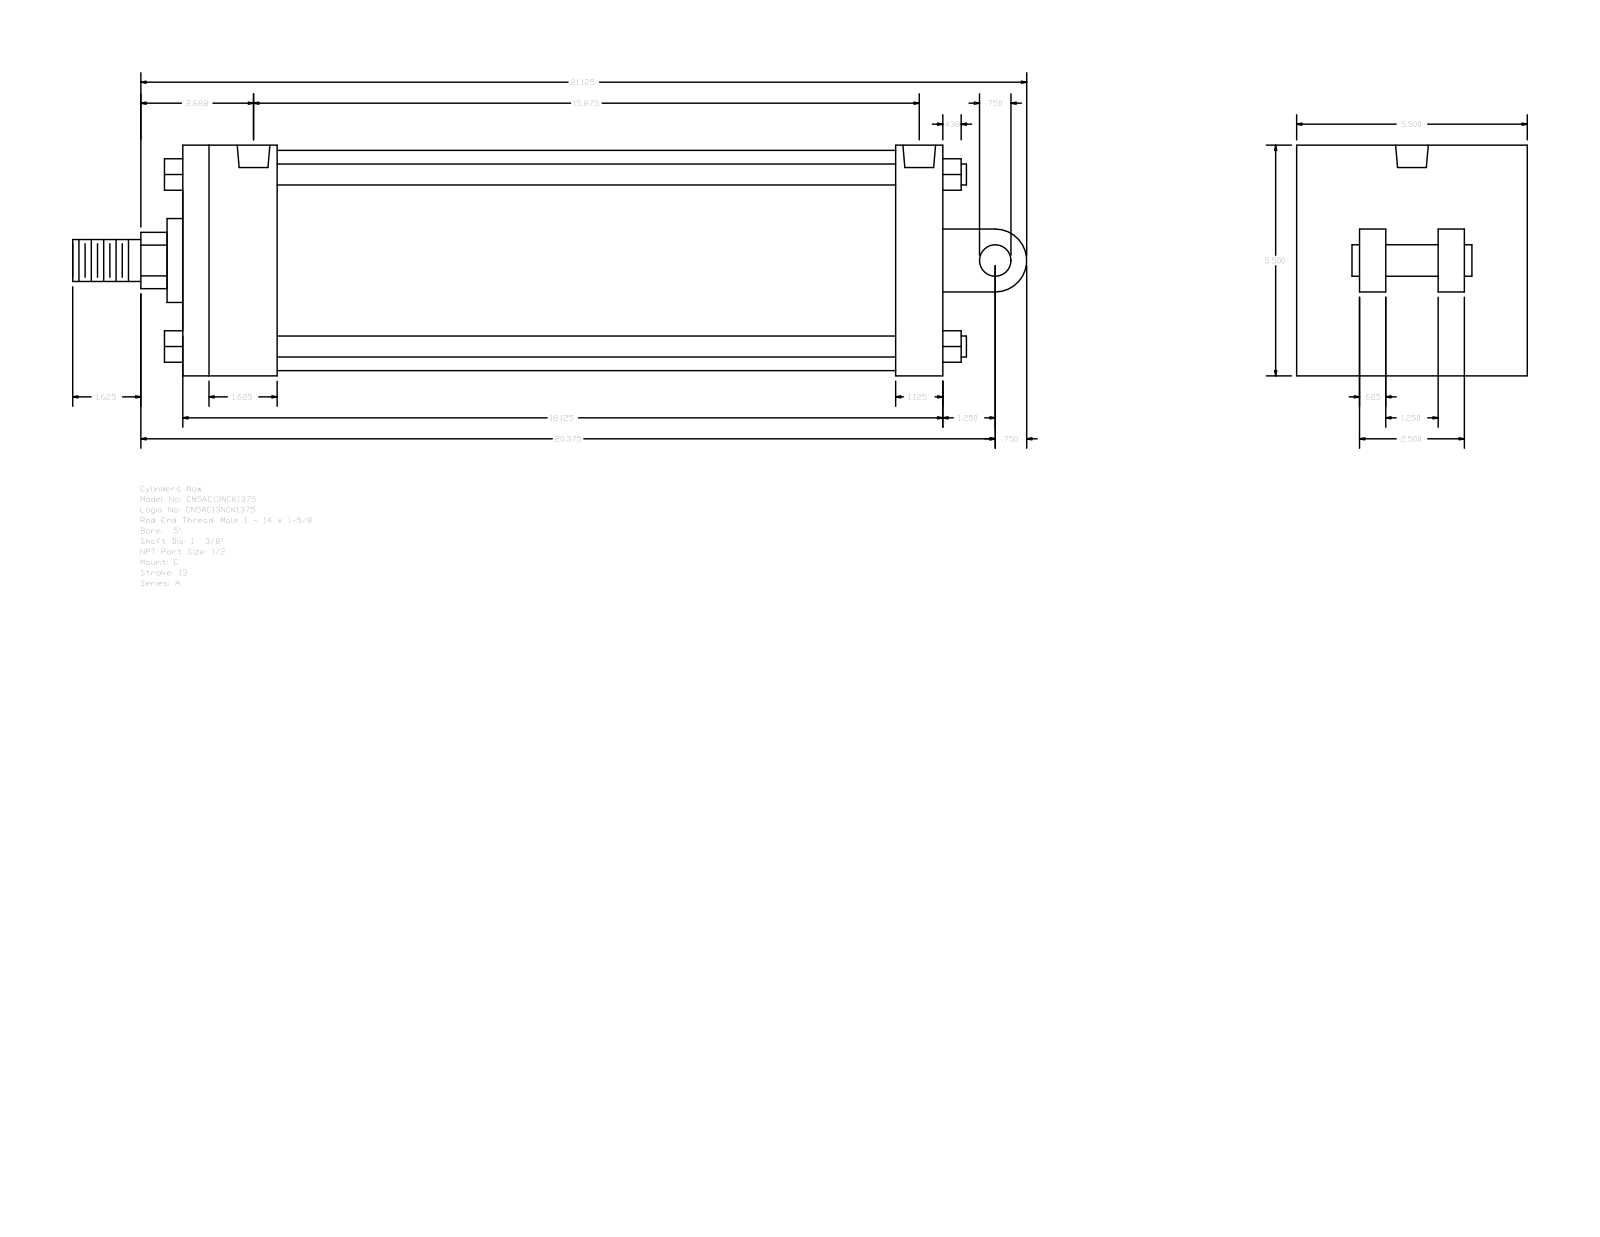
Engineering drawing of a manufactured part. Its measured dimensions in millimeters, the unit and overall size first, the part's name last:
Units: millimetres
Overall size (bounding box): 577.85 × 139.7 × 139.7
Round holes (diameter × count): ⌀8.73 ×4, ⌀19.77 ×2
Round bosses / shafts (diameter × count): ⌀12.7 ×4, ⌀133.35 ×1, ⌀50.8 ×1, ⌀34.92 ×1, ⌀25.4 ×1, ⌀19.05 ×1
Partial cylindrical surfaces — rounded edges, fillets, slot ends (radius × count): R17.06 ×1, R19.05 ×1
Main face-to-face distances: 139.7, 460.37, 57.15, 431.8, 374.65, 403.22, 28.57, 38.1, 53.97, 101.6
Hole centre spacings: 2.39, 398.45, 400.84, 403.23
Bodies: 0 solids, 135 faces (102 planar, 33 cylindrical, 0 other)
Part name (STEP PRODUCT): A_C__0500_1.375
STEP written by: GSSL Pune (CONFIG_CONTROL_DESIGN)
